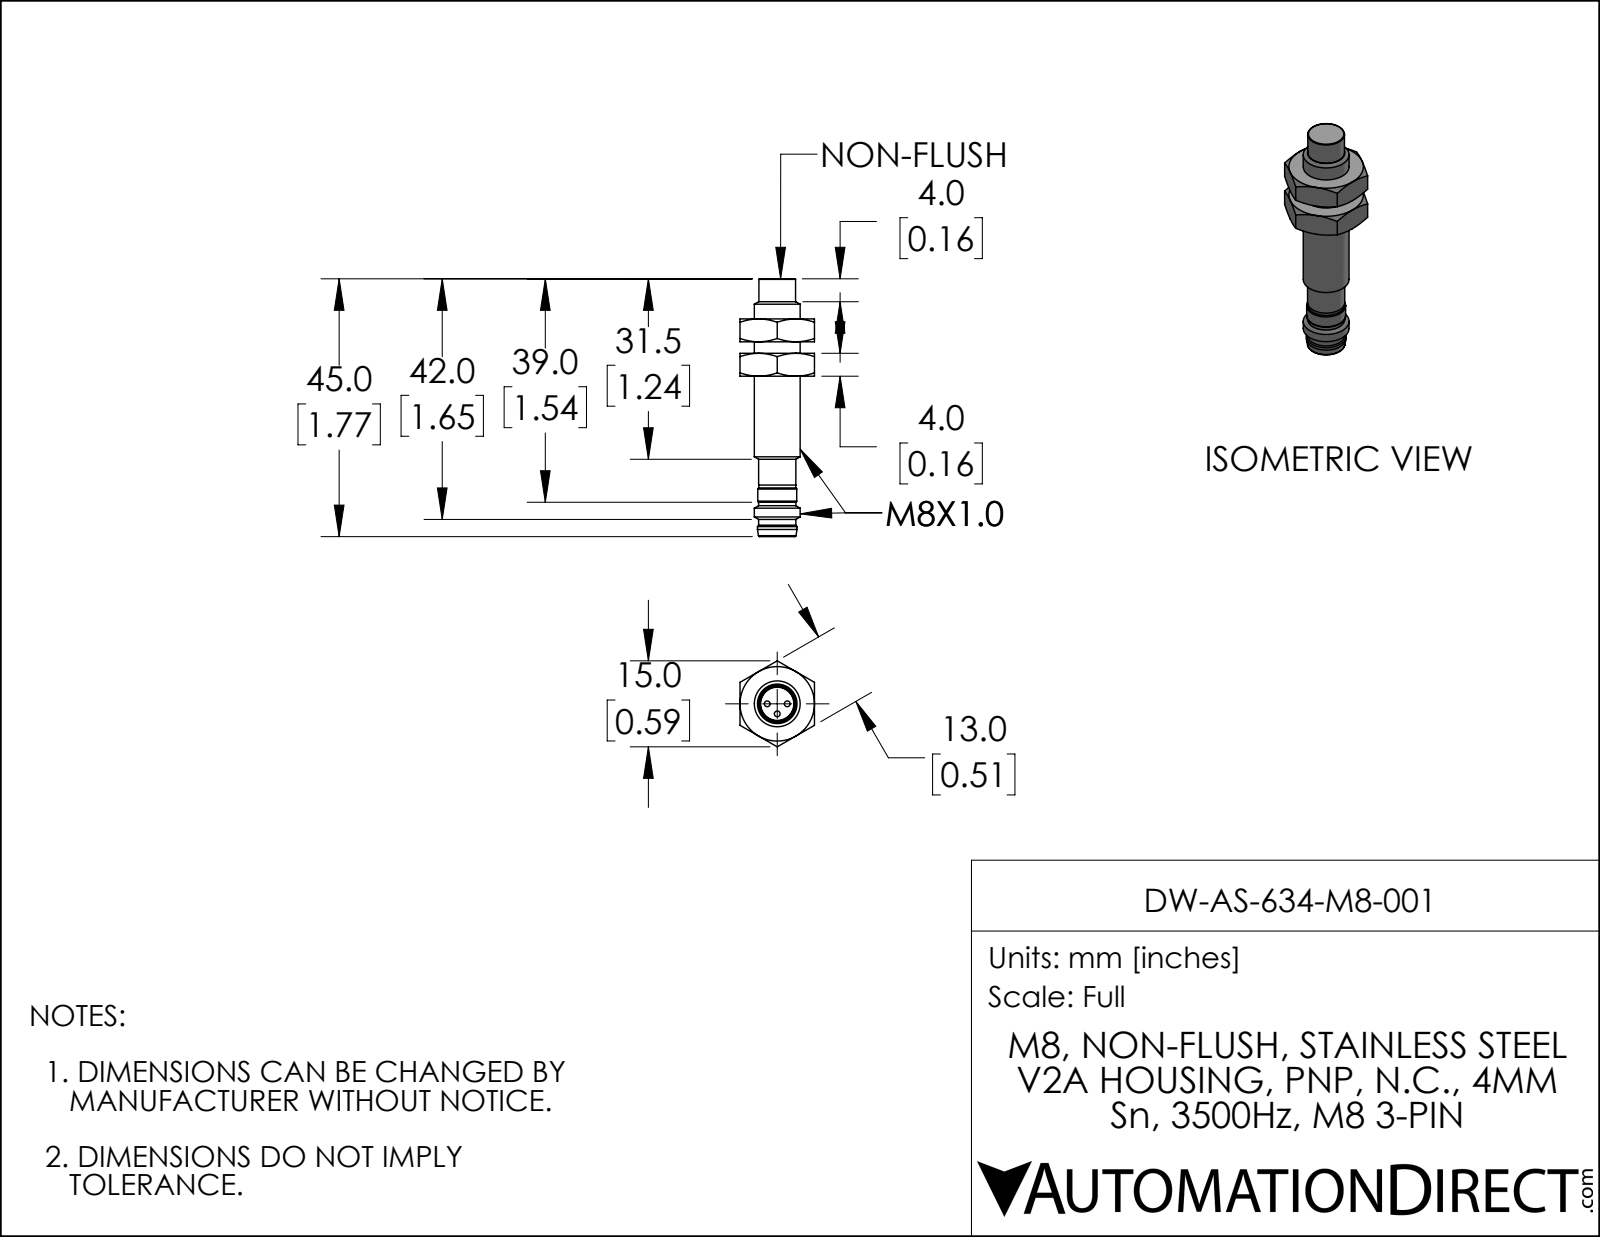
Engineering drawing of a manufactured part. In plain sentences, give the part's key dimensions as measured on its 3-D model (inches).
The part is named "DW-AS-634-M8-001". Its 3-D file was written by "SolidWorks 2019 (AUTOMOTIVE_DESIGN)". It is 1 solid with 76 faces: 24 planar, 15 cylindrical and 37 other. Overall it measures 1.772 by 0.591 by 0.512 inches. Its volume is 0.161 cubic inches and its surface area 2.817 square inches. Round holes: 1 of diameter 0.228. Round bosses or shafts: 3 of diameter 0.039, 1 of diameter 0.315, 1 of diameter 0.272, 1 of diameter 0.268, 1 of diameter 0.256, 1 of diameter 0.254, 1 of diameter 0.252. The main face-to-face distances are 0.512, 0.157, 0.236, 0.079, 0.394, 0.276, 0.433, 0.669, 1.142, 0.906.
